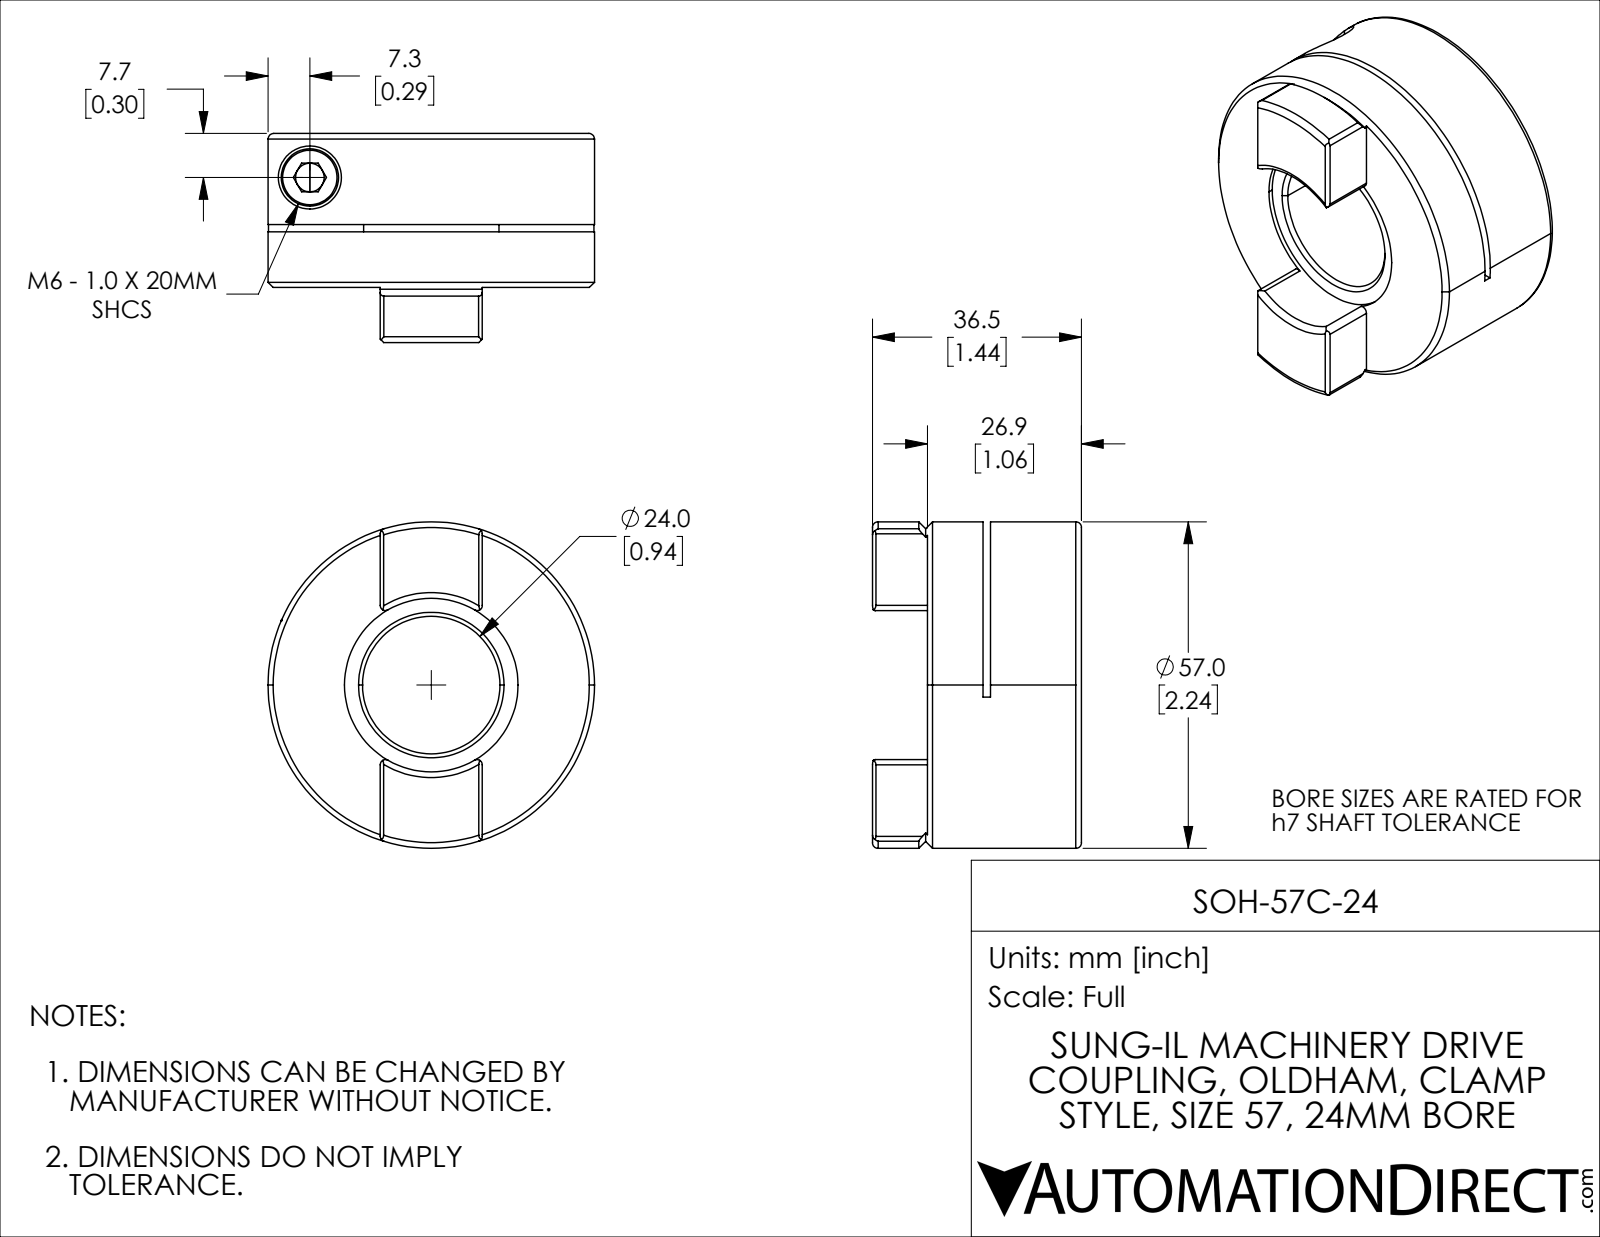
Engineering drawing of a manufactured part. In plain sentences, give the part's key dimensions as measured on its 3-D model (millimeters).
The part is named "SOH-57C-24". Its 3-D file was written by "SolidWorks 2021 (CONFIG_CONTROL_DESIGN)". It is 2 solids with 97 faces: 39 planar, 33 cylindrical and 25 other. Overall it measures 57 by 57 by 36.5 millimeters. Its volume is 58 065 cubic millimeters and its surface area 16 154 square millimeters. Round holes: 1 of diameter 5, 1 of diameter 6.4, 1 of diameter 11, 1 of diameter 24, 1 of diameter 30.3. Round bosses or shafts: 1 of diameter 57, 1 of diameter 10, 1 of diameter 6. Partial cylindrical surfaces (rounded edges, fillets, slot ends): 8 of radius 0.9, 1 of radius 40. The main face-to-face distances are 1.3, 26.9, 17.2, 9.7, 15.9, 11, 36.5, 20.6, 19.3, 9.6.
